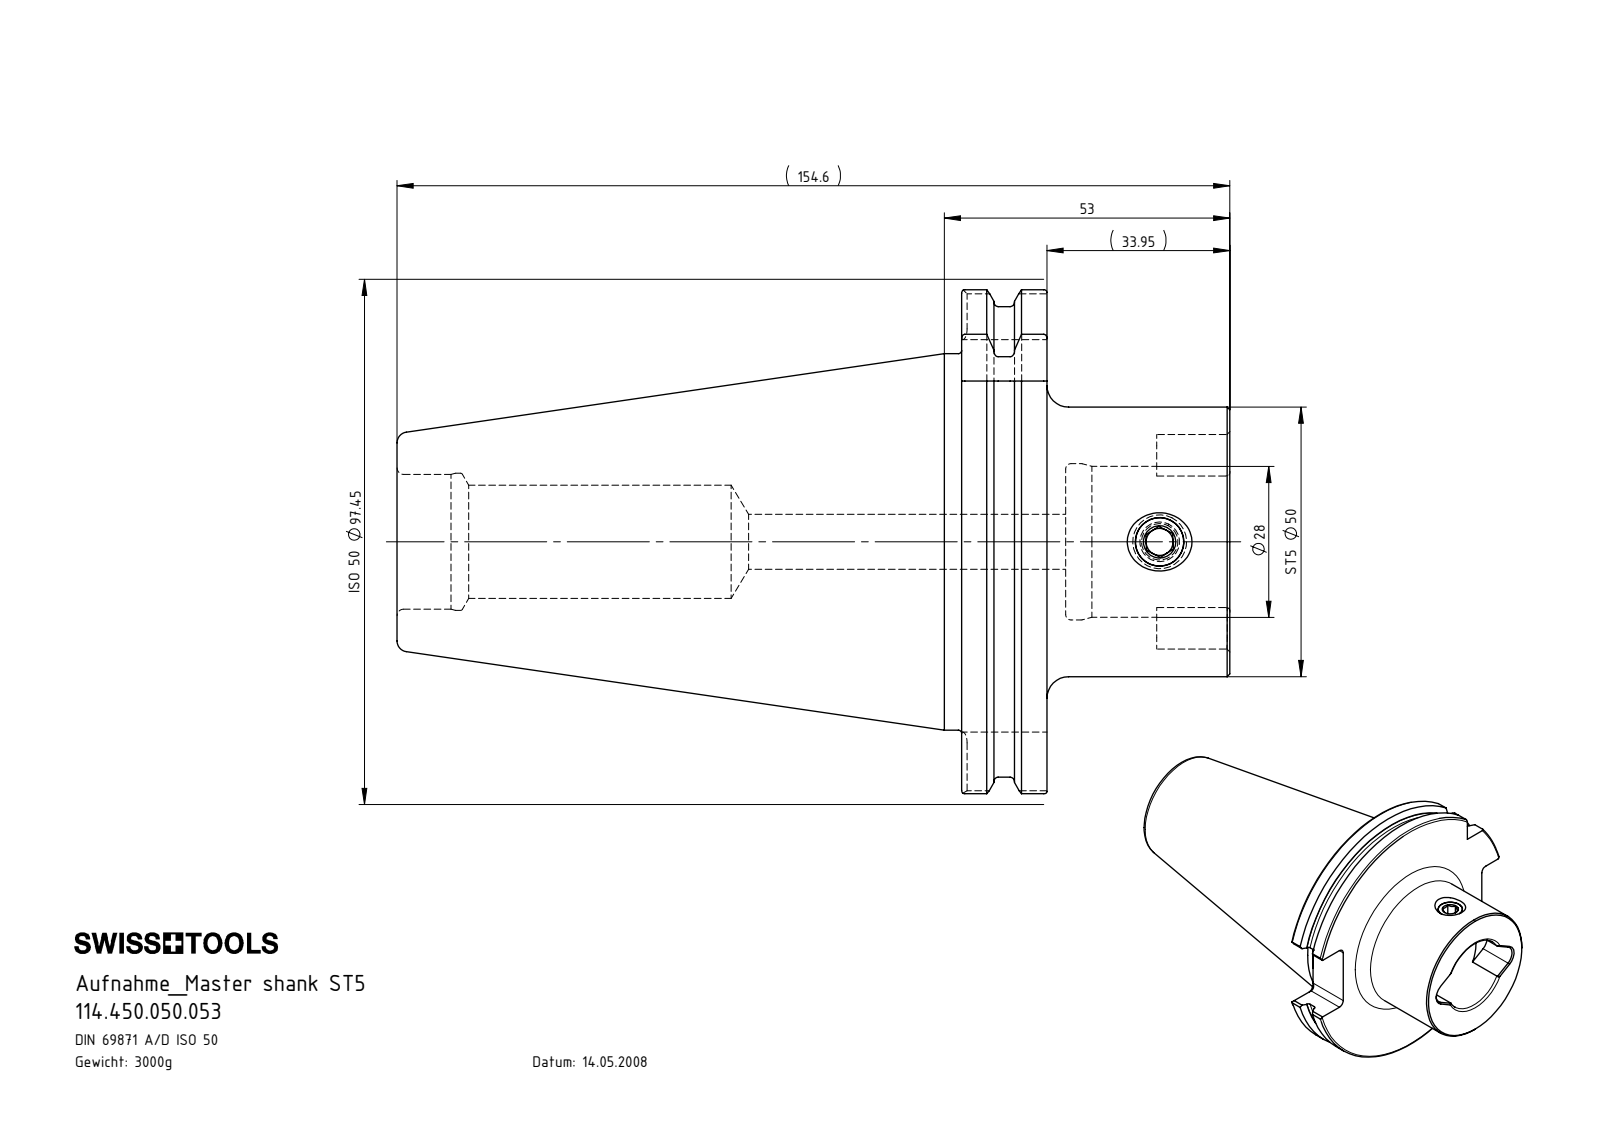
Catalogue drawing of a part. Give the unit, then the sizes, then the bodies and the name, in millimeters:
Units: millimetres
Overall size (bounding box): 154.6 × 97.45 × 93.51
Round holes (diameter × count): ⌀5 ×1, ⌀9 ×1, ⌀10.2 ×1, ⌀21 ×1, ⌀25 ×1, ⌀25.45 ×1, ⌀28 ×1, ⌀29 ×1
Round bosses / shafts (diameter × count): ⌀91 ×1, ⌀69.85 ×1, ⌀50 ×1, ⌀10 ×1
Partial cylindrical surfaces — rounded edges, fillets, slot ends (radius × count): R2 ×8, R4.2 ×2, R48.73 ×1
Main face-to-face distances: 15.85, 49.8, 33.95, 19.3, 3.45, 30.5, 104.8, 120.65, 124.1, 154.6
Volume: 382 229 mm³ · Surface area: 50 139 mm²
Bodies: 2 solids, 126 faces (54 planar, 30 cylindrical, 42 other)
Part name (STEP PRODUCT): SK5.ST5.K01.053; SK5-ST5.K01.053_B; ST5-ER1.001.012_A
STEP written by: SolidWorks 2017 (AUTOMOTIVE_DESIGN)
